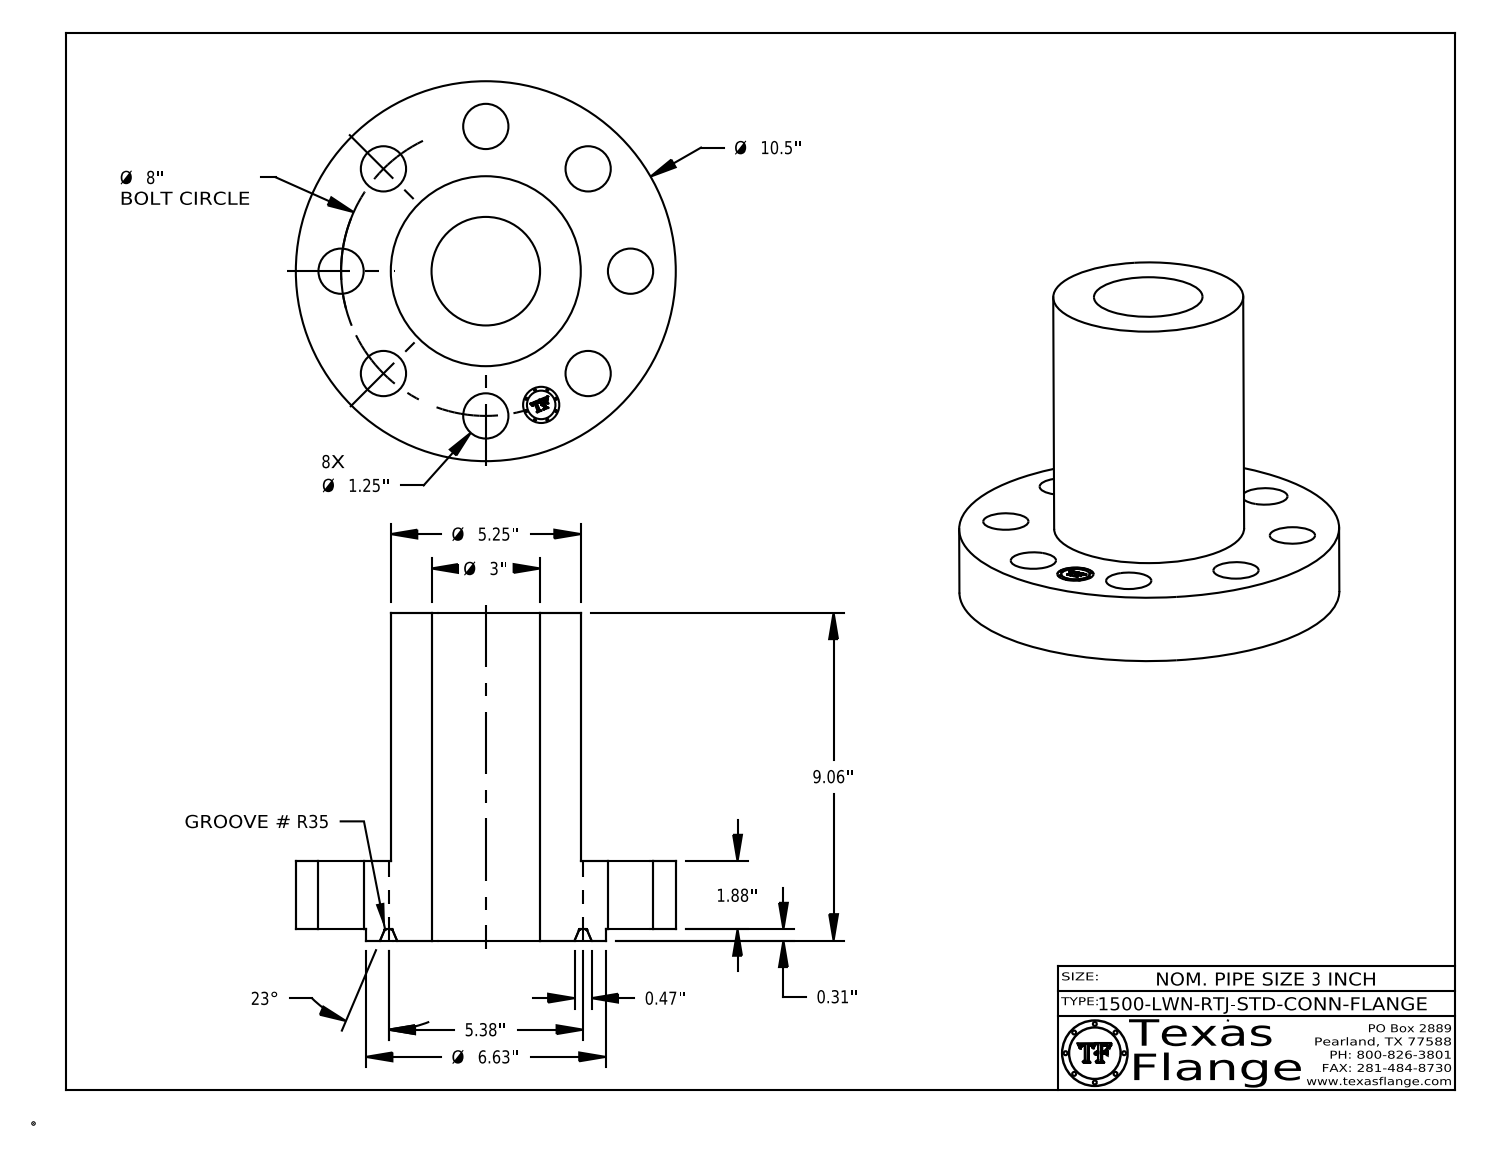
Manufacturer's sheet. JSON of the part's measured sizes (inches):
{"part_name": "3-1500-LWN-RTJ-STD-CONN-FLANGE", "step_written_by": "CATIA V5 STEP AP214 (AUTOMOTIVE_DESIGN)", "units": "inches", "bodies": {"solids": 1, "faces": 423, "planar": 371, "cylindrical": 44, "other": 8}, "overall_size": [10.5, 10.5, 9.063], "volume_in3": 238, "surface_area_in2": 472.6, "round_holes": [[1.25, 8], [1, 1], [3, 1]], "round_bosses_or_shafts": [[0.061, 8], [10.5, 1], [6.625, 1], [5.25, 1], [0.788, 1]], "face_to_face_distances": [1.88, 0.313, 2.193, 9.063, 8.75, 6.87, 2.188, 1.875, 6.875, 0.298], "hole_center_spacings": [4, 3.061, 5.657, 7.391, 1.561, 6.652, 7.846, 8]}
